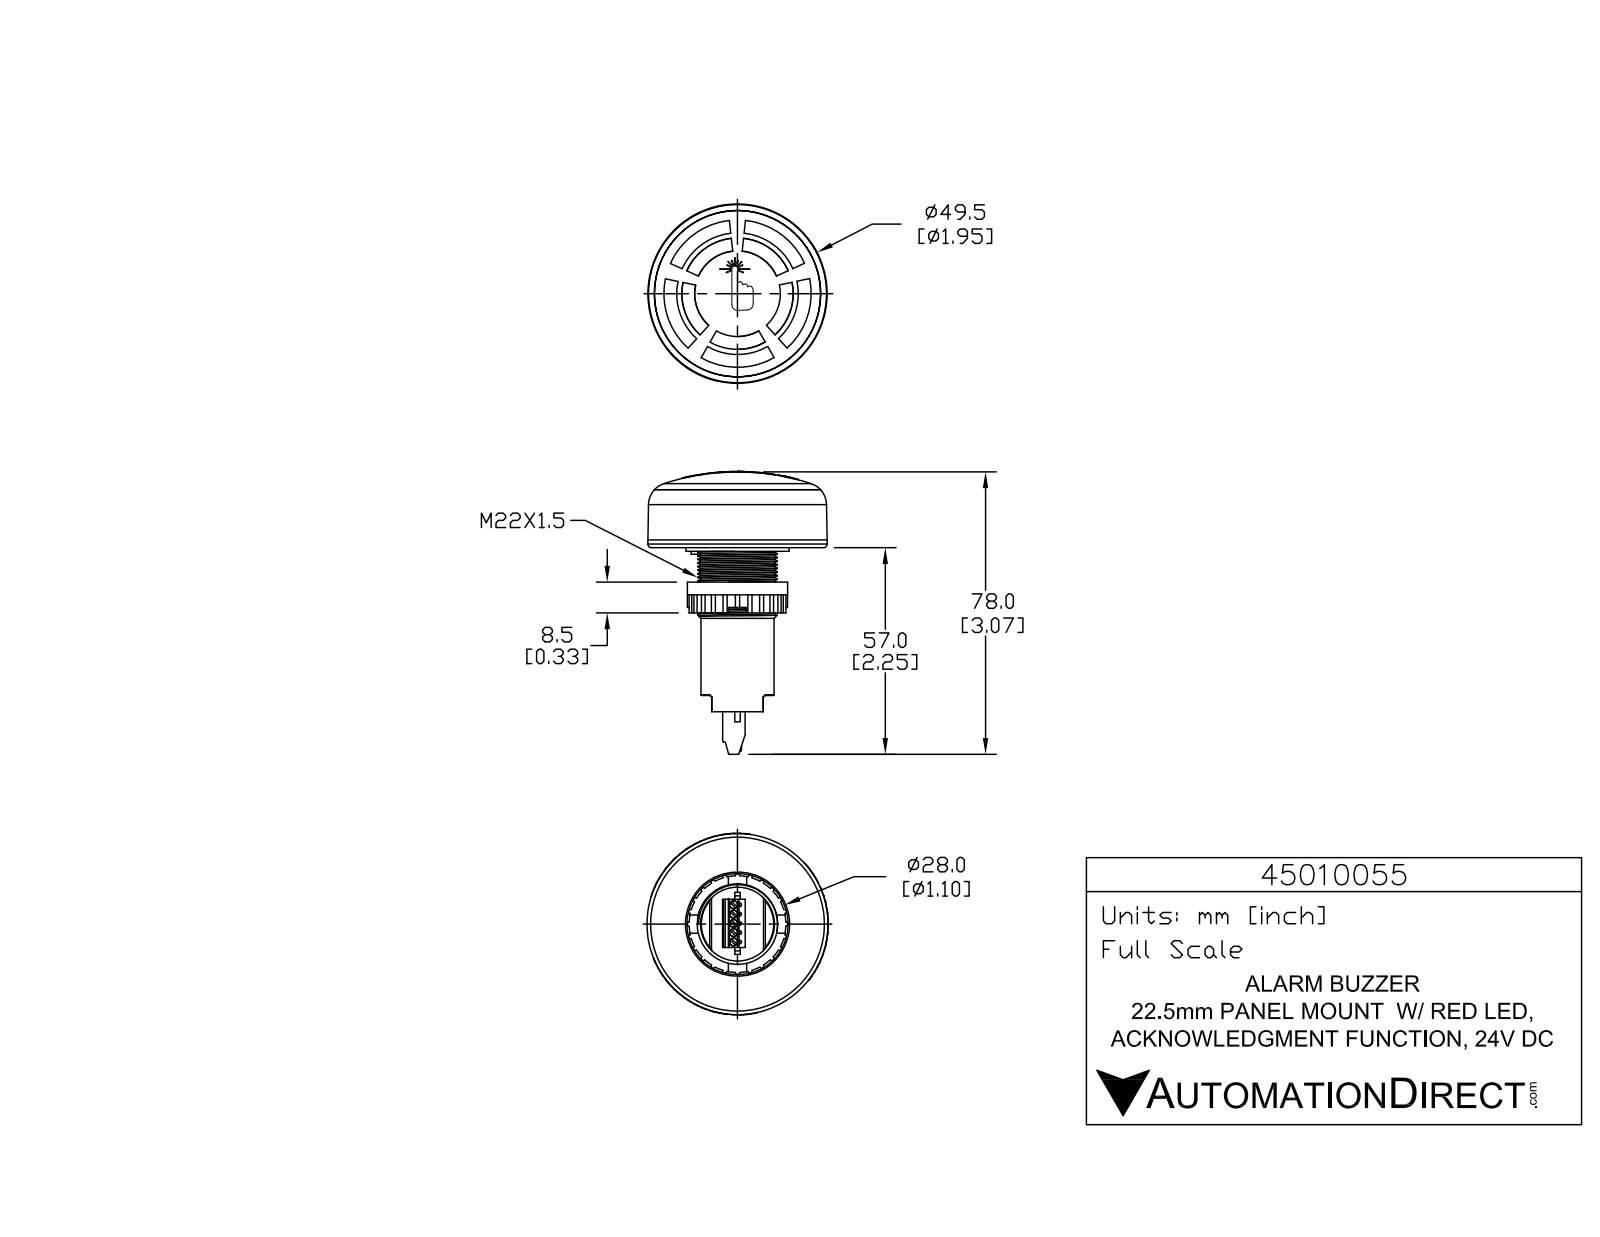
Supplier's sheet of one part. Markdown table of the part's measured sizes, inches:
| quantity | value |
| --- | --- |
| part name | 45010055 |
| STEP written by | SolidWorks 2017 (AUTOMOTIVE_DESIGN) |
| units | inches |
| bodies | 2 solids, 1335 faces (840 planar, 357 cylindrical, 138 other) |
| overall size | 3.051 × 1.956 × 1.952 |
| volume | 3.163 in³ |
| surface area | 25.78 in² |
| round holes (diameter × count) | 0.087 × 5, 0.039 × 4 |
| round bosses / shafts (diameter × count) | 0.083 × 5, 0.226 × 4, 0.056 × 4, 1.949 × 1, 1.807 × 1, 1.122 × 1, 1.091 × 1, 0.866 × 1 |
| partial cylindrical surfaces (radius × count) | 0.023 × 24, 0.02 × 16, 0.008 × 8, 0.008 × 8, 0.008 × 8, 0.131 × 8, 0.004 × 4, 0.005 × 4 |
| main face-to-face distances | 0.085, 0.335, 0.039, 0.124, 0.459, 0.374, 1.398, 1.732, 1.772, 1.856 |
| hole center spacings | 0.1, 0.2, 0.3, 0.275, 0.284, 0.302, 0.324, 0.387 |
